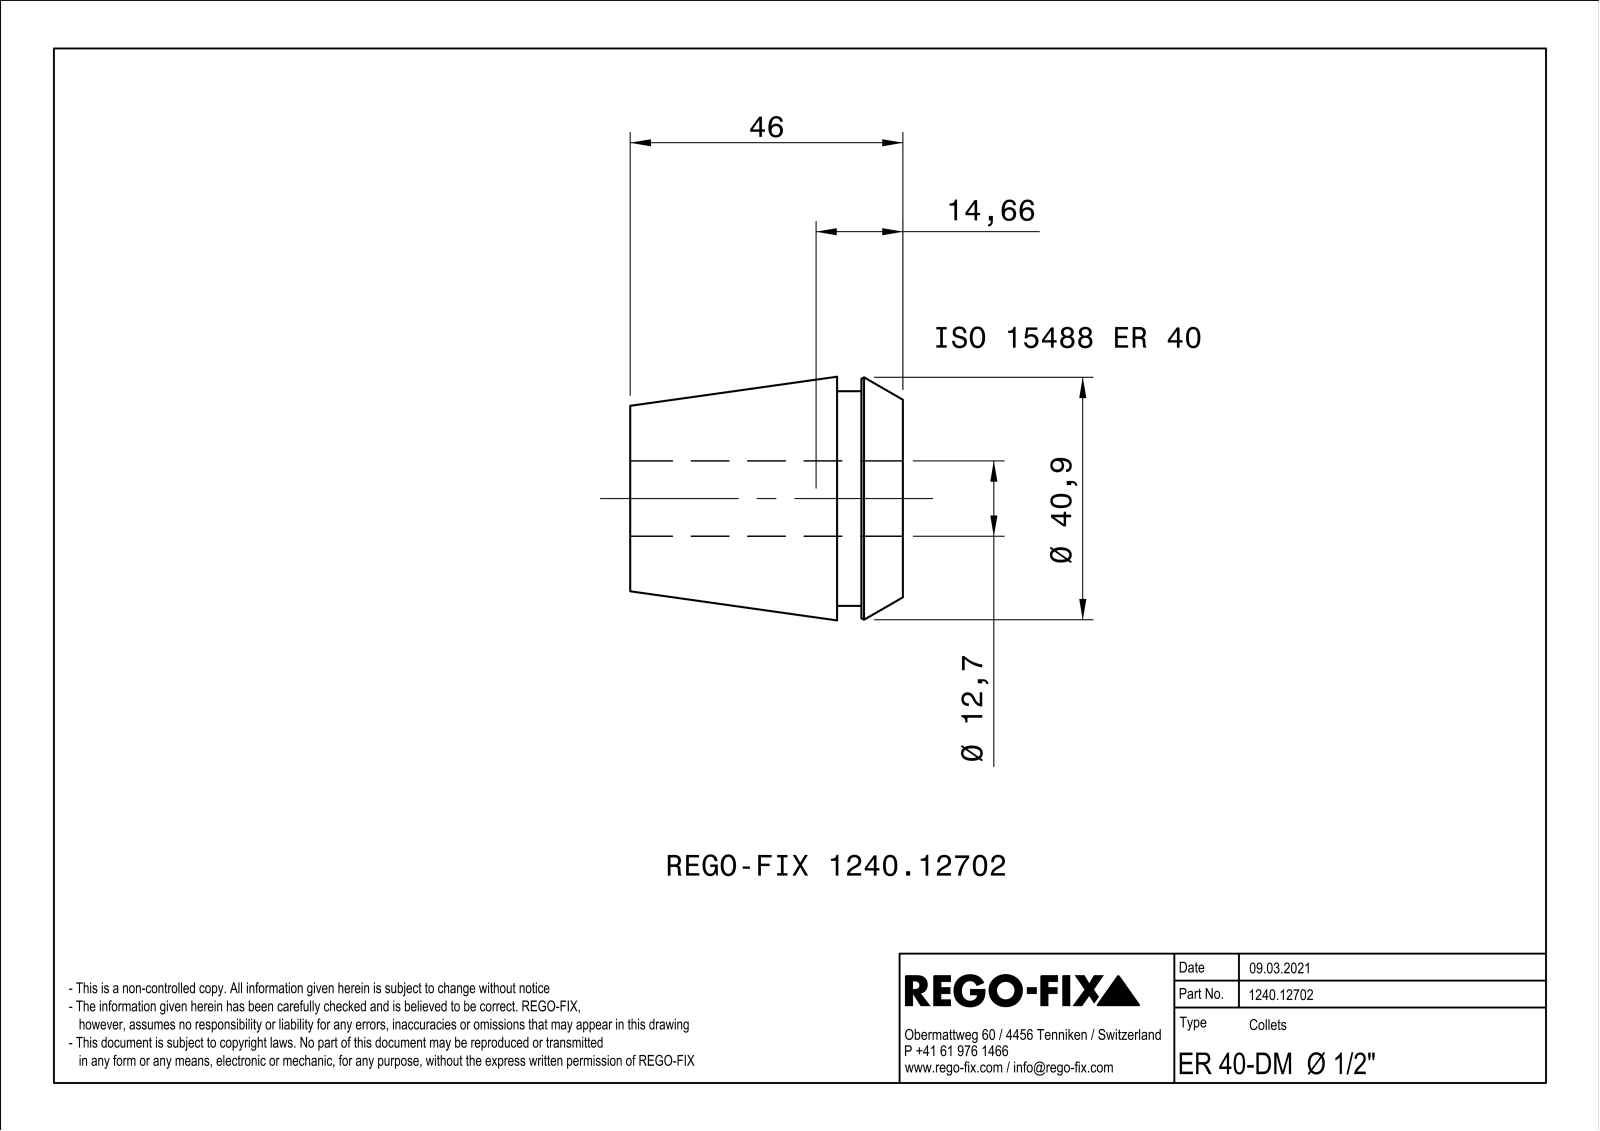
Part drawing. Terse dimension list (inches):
name: NOCUT
written by: SIEMENS PLM Software Solid Edge ST10 (AUTOMOTIVE_DESIGN)
unit: in
bodies: 1 solid, 154 faces (80 planar, 9 cylindrical, 65 other)
size: 1.811 × 1.614 × 1.614
volume: 2.162 in³; area: 32.79 in²
holes: 1× ⌀0.5
bosses: 1× ⌀1.425
face distances: 0.039, 1.811, 0.437, 1.374, 0.276, 0.161, 1.535, 0.669, 0.394, 0.232
